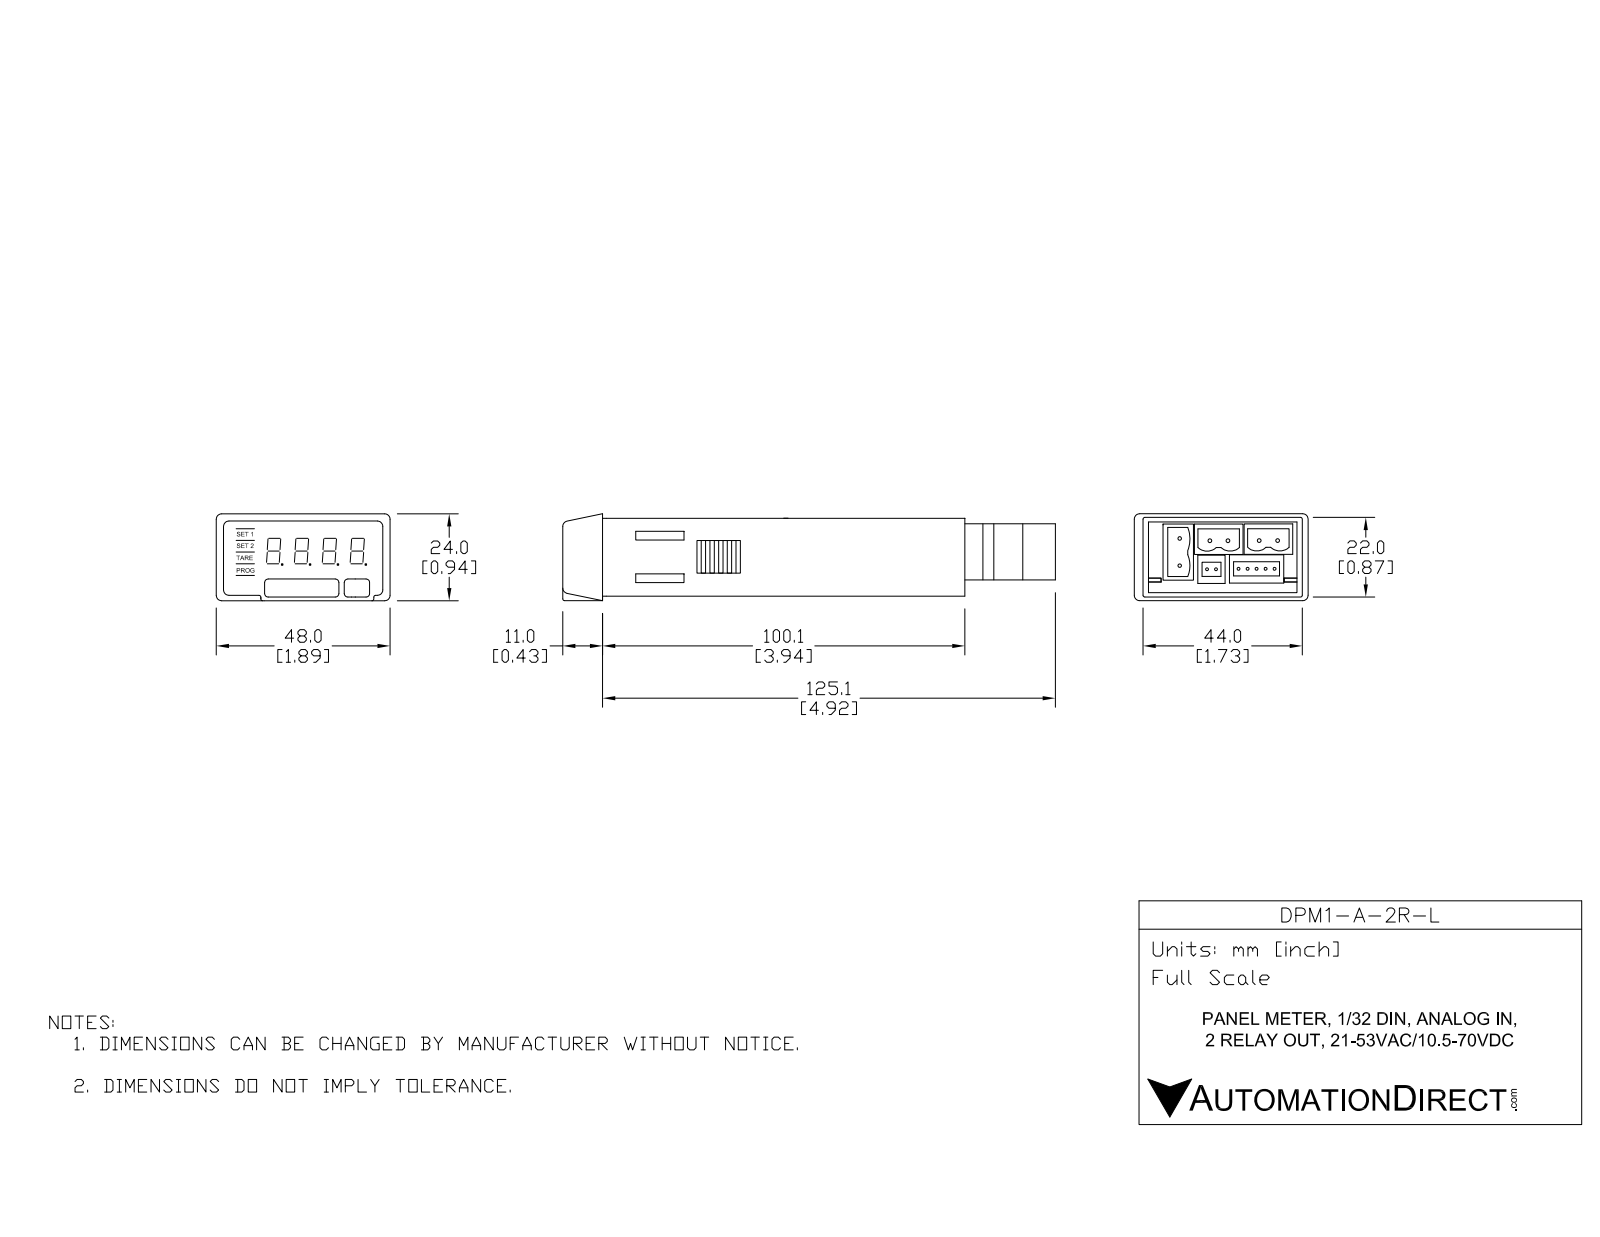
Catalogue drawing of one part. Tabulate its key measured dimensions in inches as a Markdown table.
| quantity | value |
| --- | --- |
| part name | DPM1-A-2R-L |
| STEP written by | SolidWorks 2017 (AUTOMOTIVE_DESIGN) |
| units | inches |
| bodies | 6 solids, 1467 faces (1124 planar, 167 cylindrical, 176 other) |
| overall size | 5.354 × 1.89 × 0.98 |
| volume | 2.573 in³ |
| surface area | 60.7 in² |
| round holes (diameter × count) | 0.039 × 7, 0.079 × 7, 0.078 × 6, 0.118 × 6, 0.152 × 6 |
| partial cylindrical surfaces (radius × count) | 0.012 × 14, 0.014 × 14, 0.02 × 14, 0.07 × 7, 0.072 × 7, 0.121 × 6, 0.039 × 4, 0.025 × 2 |
| main face-to-face distances | 0.059, 0.807, 0.866, 0.748, 1.673, 1.732, 1.614, 0.051, 0.433, 4.315 |
| hole center spacings | 0.54, 0.138, 0.197, 0.197, 0.201, 0.201, 0.276, 0.286 |
